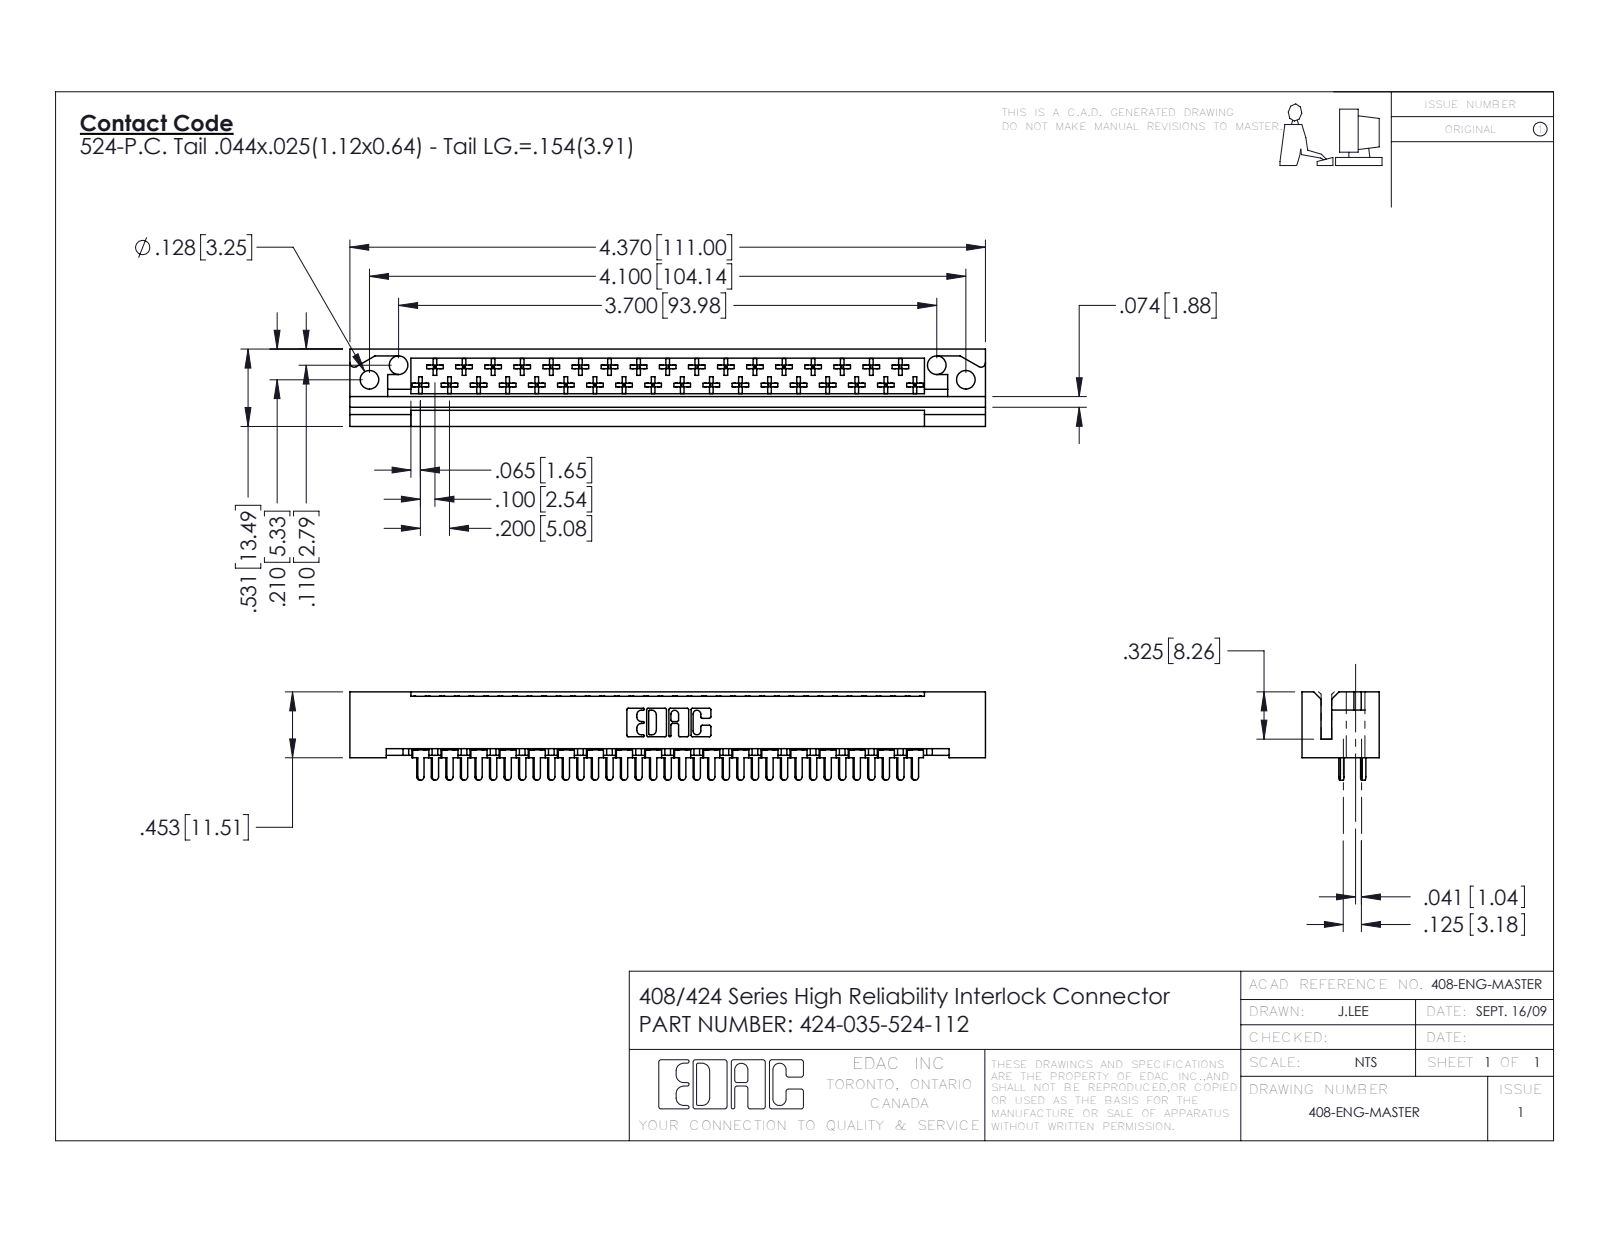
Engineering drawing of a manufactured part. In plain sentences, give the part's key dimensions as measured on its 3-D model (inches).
The part is named "424 Part_035; 408-290-001_408-290-124 - Bottom; 408-290-001_408-290-124 - Top; 424-035-524-112". Its 3-D file was written by "SolidWorks 2016 (CONFIG_CONTROL_DESIGN)". It is 36 solids with 2070 faces: 1559 planar, 371 cylindrical and 140 other. Overall it measures 4.37 by 0.607 by 0.531 inches. Its volume is 0.741 cubic inches and its surface area 23.29 square inches. Round holes: 4 of diameter 0.128. Partial cylindrical surfaces (rounded edges, fillets, slot ends): 210 of radius 0.01, 37 of radius 0.02, 35 of radius 0.022, 22 of radius 0.01, 6 of radius 0.007, 6 of radius 0.031, 3 of radius 0.026, 2 of radius 0.03. The main face-to-face distances are 0.025, 0.531, 0.4, 0.125, 0.1, 0.025, 0.217, 0.272, 0.235, 0.259. The hole center spacings are 0.224, 3.901, 3.7, 4.1.
